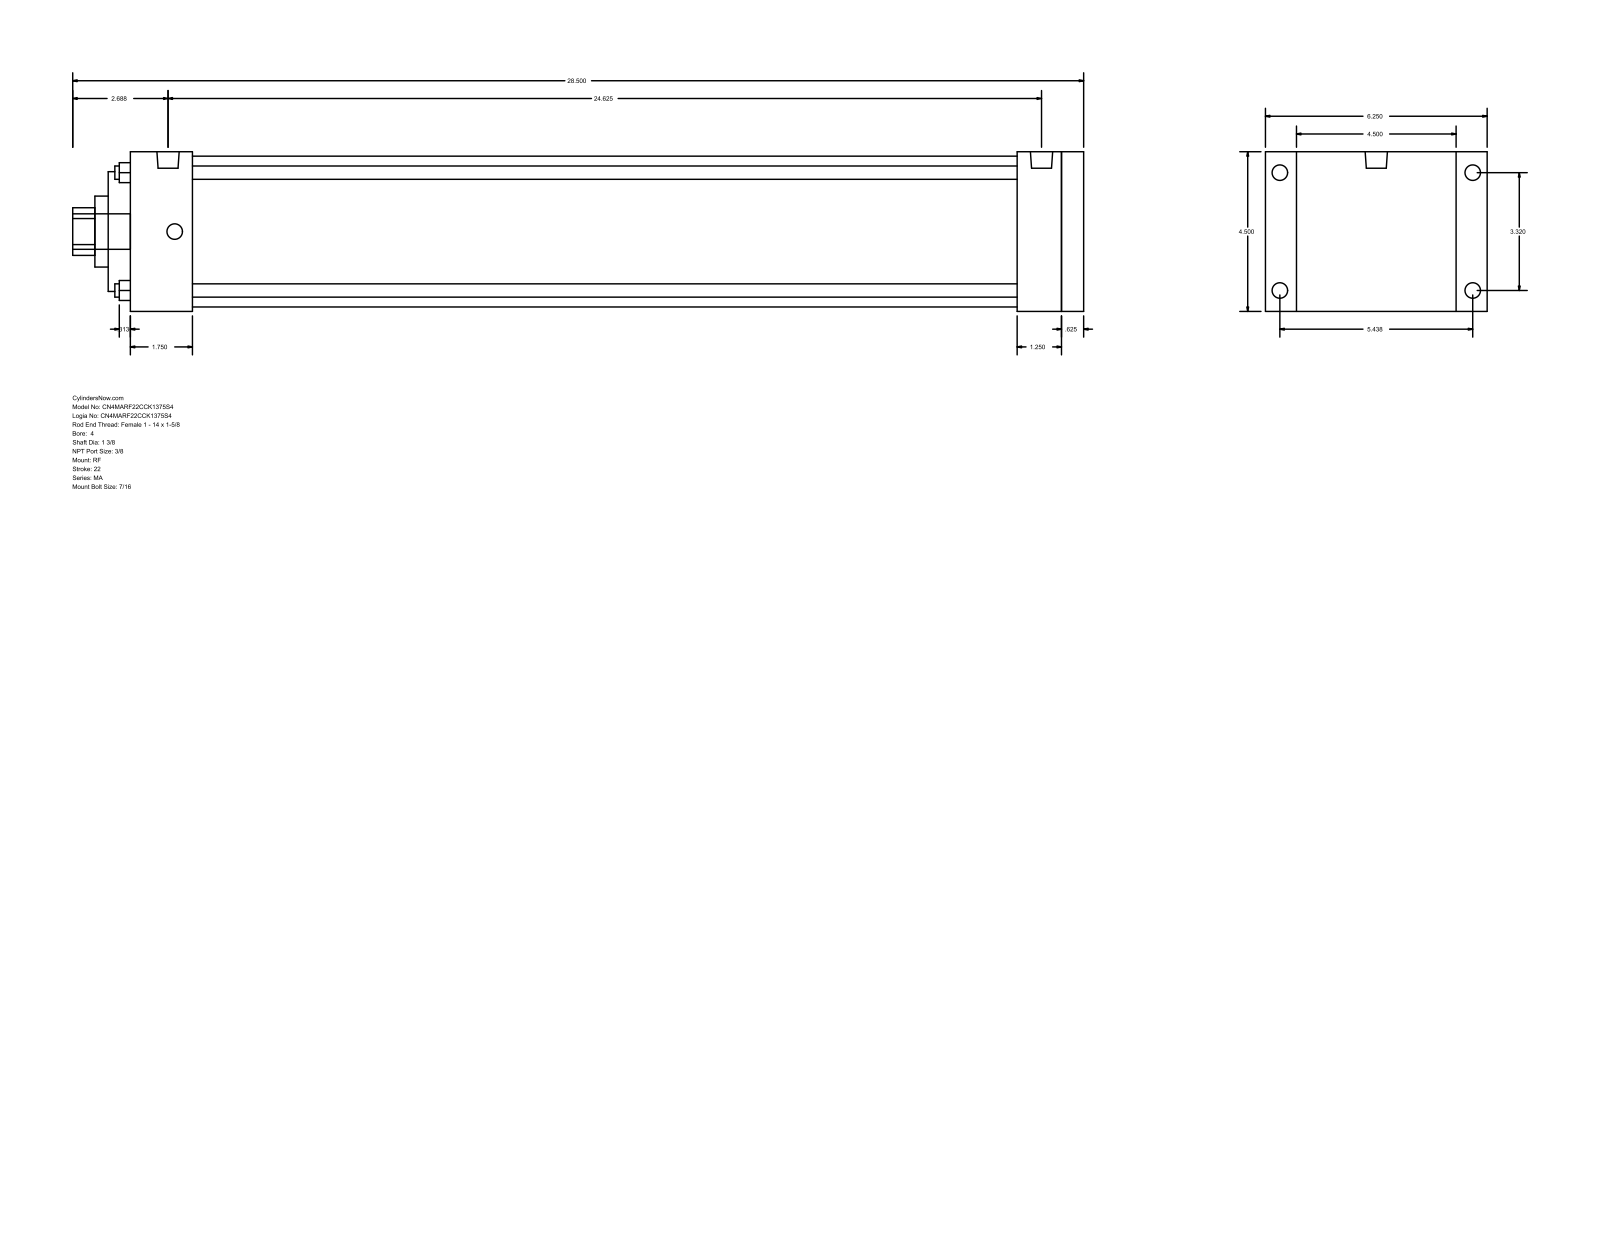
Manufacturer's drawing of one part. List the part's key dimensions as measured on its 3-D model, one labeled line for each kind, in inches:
Part name (STEP PRODUCT): MA_RF__0400_1.375
STEP written by: GSSL Pune (CONFIG_CONTROL_DESIGN)
Units: inches
Bodies: 0 solids, 94 faces (65 planar, 29 cylindrical, 0 other)
Overall size (bounding box): 28.5 × 6.25 × 4.5
Round holes (diameter × count): ⌀0.375 ×4, ⌀1.375 ×1, ⌀2 ×1, ⌀3.375 ×1, ⌀4.25 ×1
Round bosses / shafts (diameter × count): ⌀0.437 ×8, ⌀0.627 ×2, ⌀1 ×1
Partial cylindrical surfaces — rounded edges, fillets, slot ends (radius × count): R0.672 ×1
Main face-to-face distances: 4.5, 26.875, 0.625, 26.25, 0.625, 26.875, 27.5, 0.875, 5.375, 25.625
Hole centre spacings: 2.347, 3.32, 4.695
